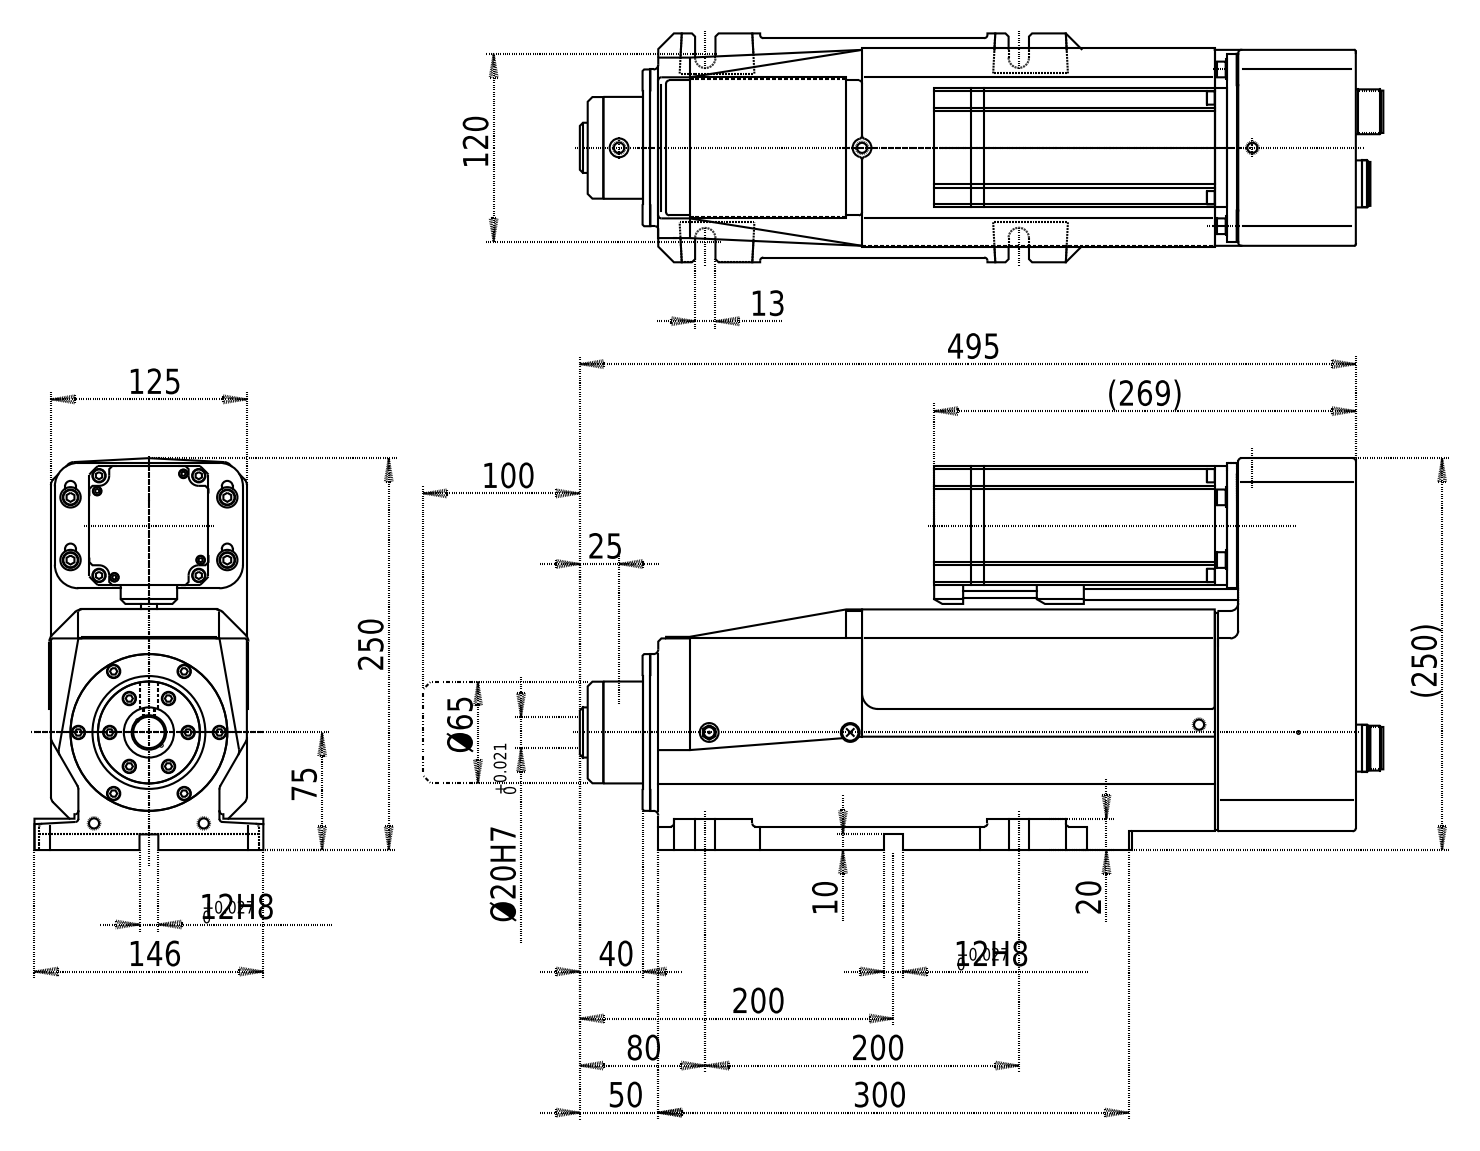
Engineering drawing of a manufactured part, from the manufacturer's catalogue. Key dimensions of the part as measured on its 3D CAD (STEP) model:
Part name (STEP PRODUCT): JPU-504O`}
STEP written by: SolidWorks 2006104 (CONFIG_CONTROL_DESIGN)
Units: millimetres
Bodies: 2 solids, 271 faces (177 planar, 86 cylindrical, 8 other)
Overall size (bounding box): 495 × 250 × 146
Volume: 9 993 000 mm³ · Surface area: 441 334 mm²
Round holes (diameter × count): ⌀12 ×2, ⌀20 ×1, ⌀21 ×1
Round bosses / shafts (diameter × count): ⌀100 ×1, ⌀65 ×1, ⌀32 ×1
Partial cylindrical surfaces — rounded edges, fillets, slot ends (radius × count): R2 ×17, R5 ×17, R4 ×10, R6.5 ×8, R10 ×5, R3 ×4, R15 ×4, R50 ×1
Main face-to-face distances: 125, 1, 126, 153.5, 18.5, 12, 17.5, 76, 10, 133.5
Hole centre spacings: 155
